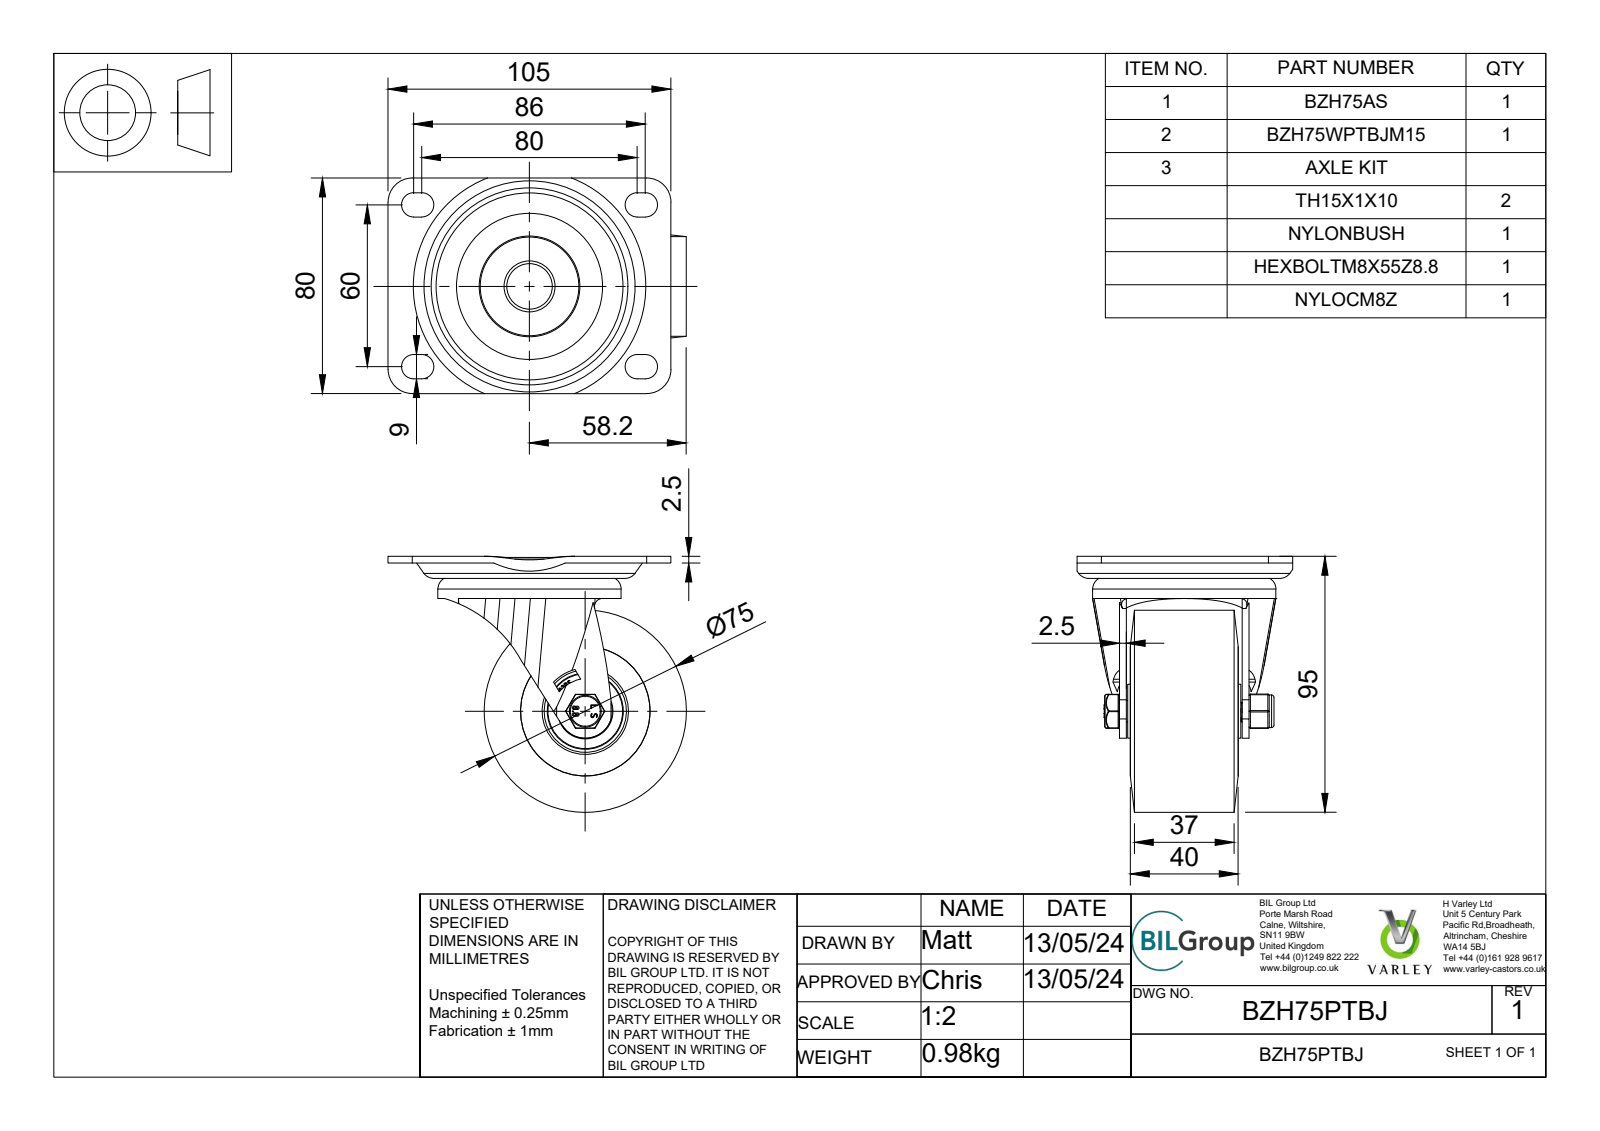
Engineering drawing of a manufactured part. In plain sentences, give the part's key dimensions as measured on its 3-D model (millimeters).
The part is named "BZH75PTBJ v3; BZH75AS v1; ZINC PLATED, PRESSED STEEL TOP PLATE; ZINC PLATED, PRESSED STEEL FORKS (+7 more)". Its 3-D file was written by "Autodesk Translation Framework v12.20.1.177 (AUTOMOTIVE_DESIGN)". It is 40 solids with 1127 faces: 375 planar, 222 cylindrical and 530 other. Overall it measures 110.7 by 95 by 80 millimeters. Its volume is 206 922 cubic millimeters and its surface area 95 518 square millimeters. Round holes: 2 of diameter 0.66, 1 of diameter 8, 1 of diameter 8.2, 1 of diameter 8.6, 1 of diameter 10.25, 1 of diameter 14, 1 of diameter 15, 1 of diameter 15.5, 1 of diameter 20.5, 1 of diameter 26.8, 1 of diameter 28, 1 of diameter 28.2. Round bosses or shafts: 1 of diameter 75, 1 of diameter 68, 1 of diameter 24, 1 of diameter 21.5, 1 of diameter 20, 1 of diameter 19, 1 of diameter 18.91, 1 of diameter 18. Partial cylindrical surfaces (rounded edges, fillets, slot ends): 18 of radius 0.5, 12 of radius 0.25, 8 of radius 4.5, 4 of radius 0.33, 4 of radius 0.64, 4 of radius 9, 2 of radius 0.63, 2 of radius 0.64. The main face-to-face distances are 2.5, 7.26, 0.4, 1.5, 31, 40, 2.4, 9.76, 0.5, 4.04. The hole center spacings are 3.22, 2.49.
